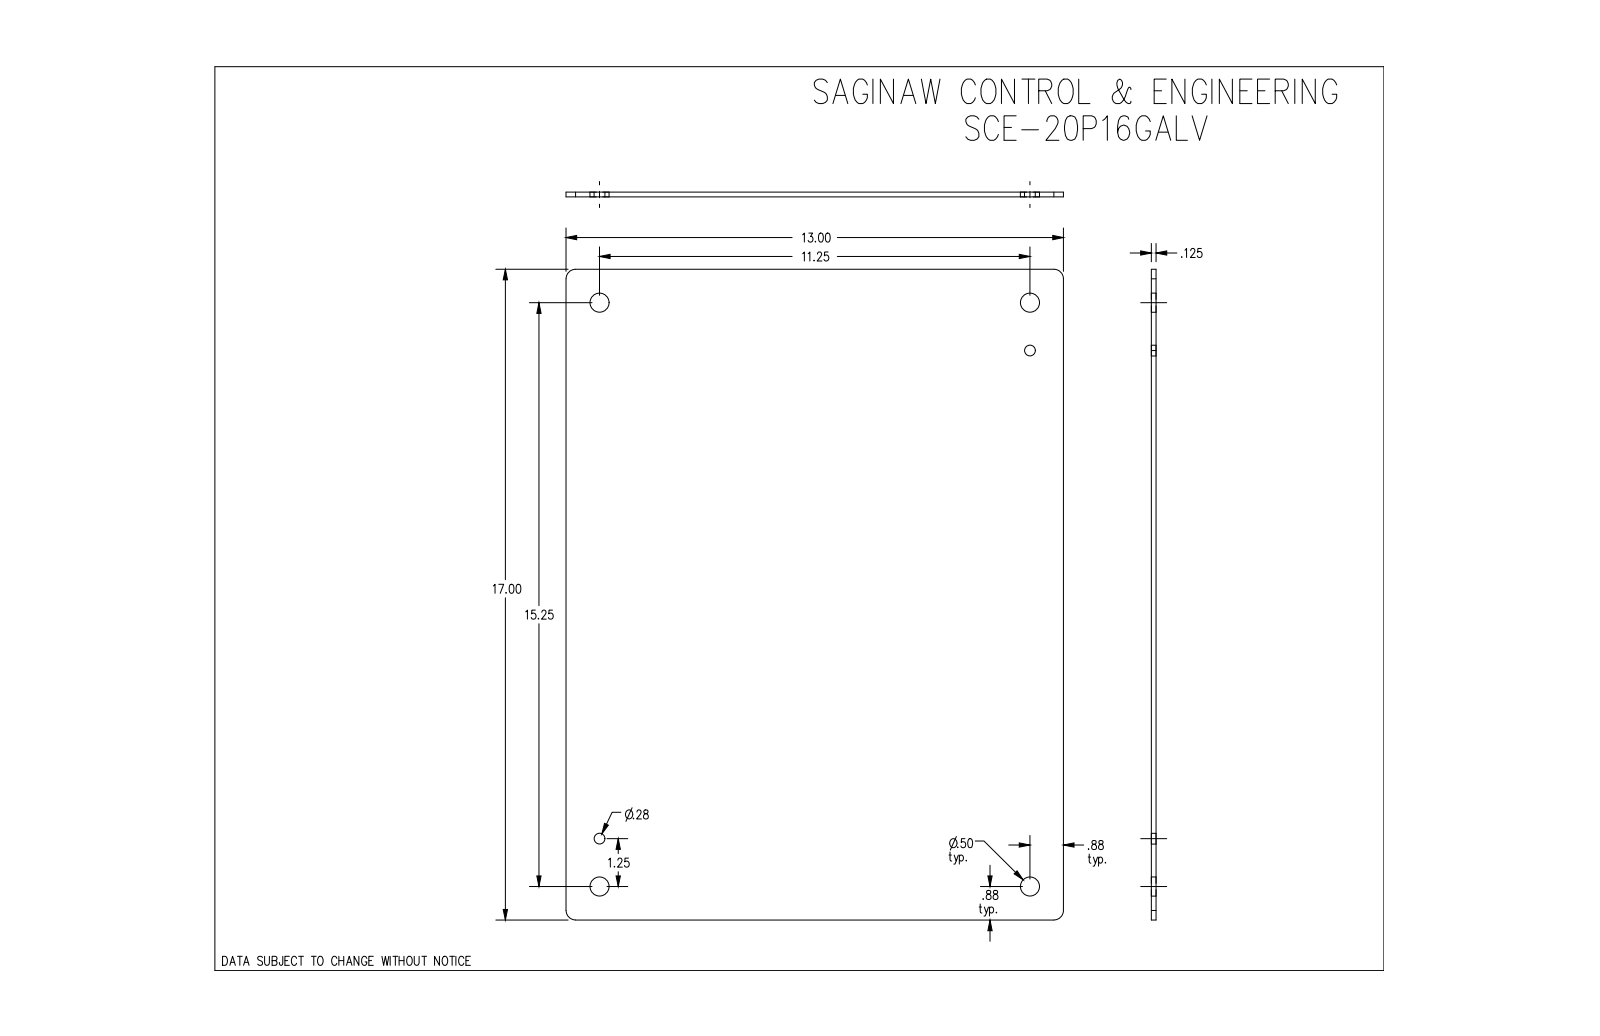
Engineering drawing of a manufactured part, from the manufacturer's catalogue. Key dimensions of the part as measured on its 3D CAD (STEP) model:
Part name (STEP PRODUCT): SCE-20P16GALV
STEP written by: SolidWorks 2019 (CONFIG_CONTROL_DESIGN)
Units: inches
Bodies: 1 solid, 16 faces (6 planar, 10 cylindrical, 0 other)
Overall size (bounding box): 17 × 13 × 0.125
Volume: 27.5 in³ · Surface area: 448.5 in²
Round holes (diameter × count): ⌀0.5 ×4, ⌀0.281 ×1, ⌀0.281 ×1
Partial cylindrical surfaces — rounded edges, fillets, slot ends (radius × count): R0.25 ×4
Main face-to-face distances: 0.125, 13, 17
Hole centre spacings: 1.25, 11.25, 11.32, 14, 15.25, 17.96, 18.95, 17.004
